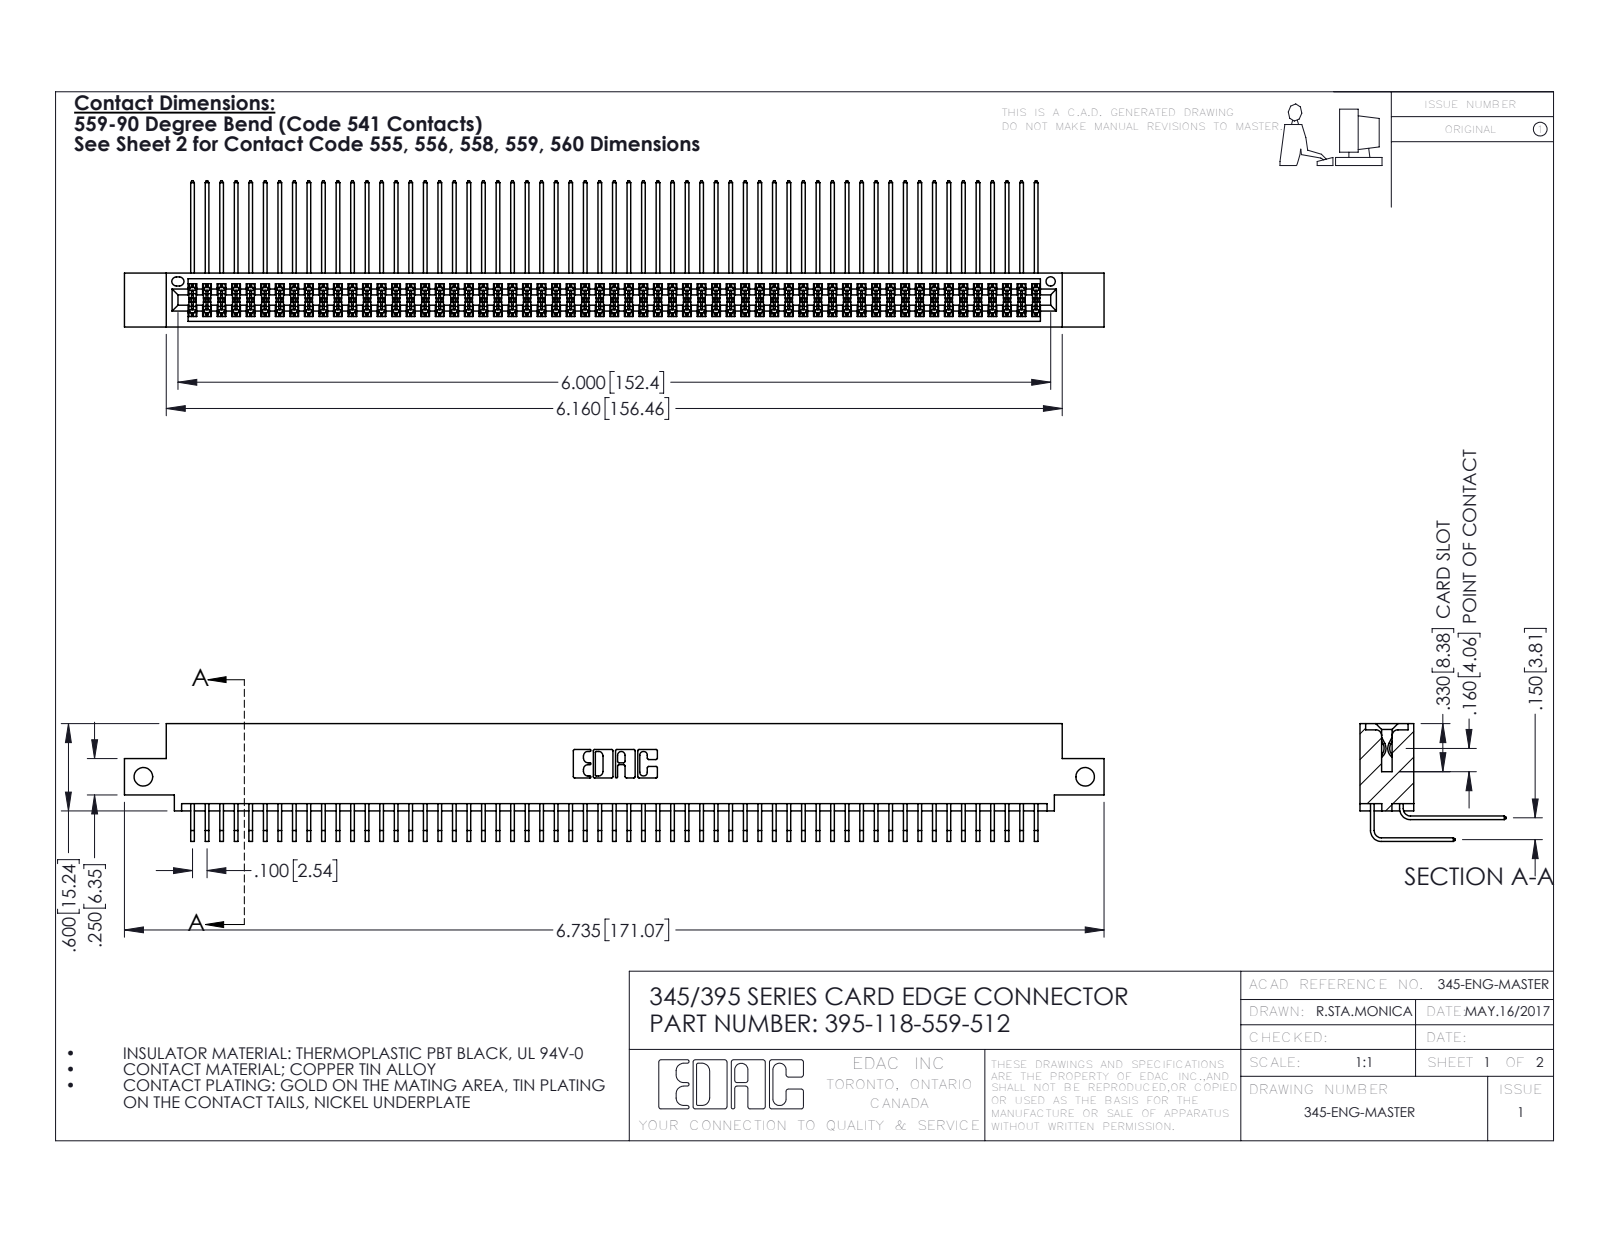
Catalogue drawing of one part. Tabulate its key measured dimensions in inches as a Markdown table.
| quantity | value |
| --- | --- |
| part name | 345-292-001_559 Tail - 2; 345-292-001_558 559 Tail - 1; 345 Part_0.110 Offset - Side Mount; 395-118-559-512 |
| STEP written by | SolidWorks 2016 (CONFIG_CONTROL_DESIGN) |
| units | inches |
| bodies | 119 solids, 6266 faces (4214 planar, 2052 cylindrical, 0 other) |
| overall size | 6.735 × 1.005 × 0.809 |
| volume | 1.055 in³ |
| surface area | 45.03 in² |
| round holes (diameter × count) | 0.128 × 2, 0.064 × 1 |
| partial cylindrical surfaces (radius × count) | 0.006 × 177, 0.01 × 22, 0.007 × 6, 0.031 × 6, 0.026 × 3, 0.014 × 2, 0.019 × 2, 0.022 × 2 |
| main face-to-face distances | 0.072, 0.298, 0.2, 0.37, 0.098, 0.272, 0.025, 0.225, 0.175, 0.15 |
| hole center spacings | 6.475 |
